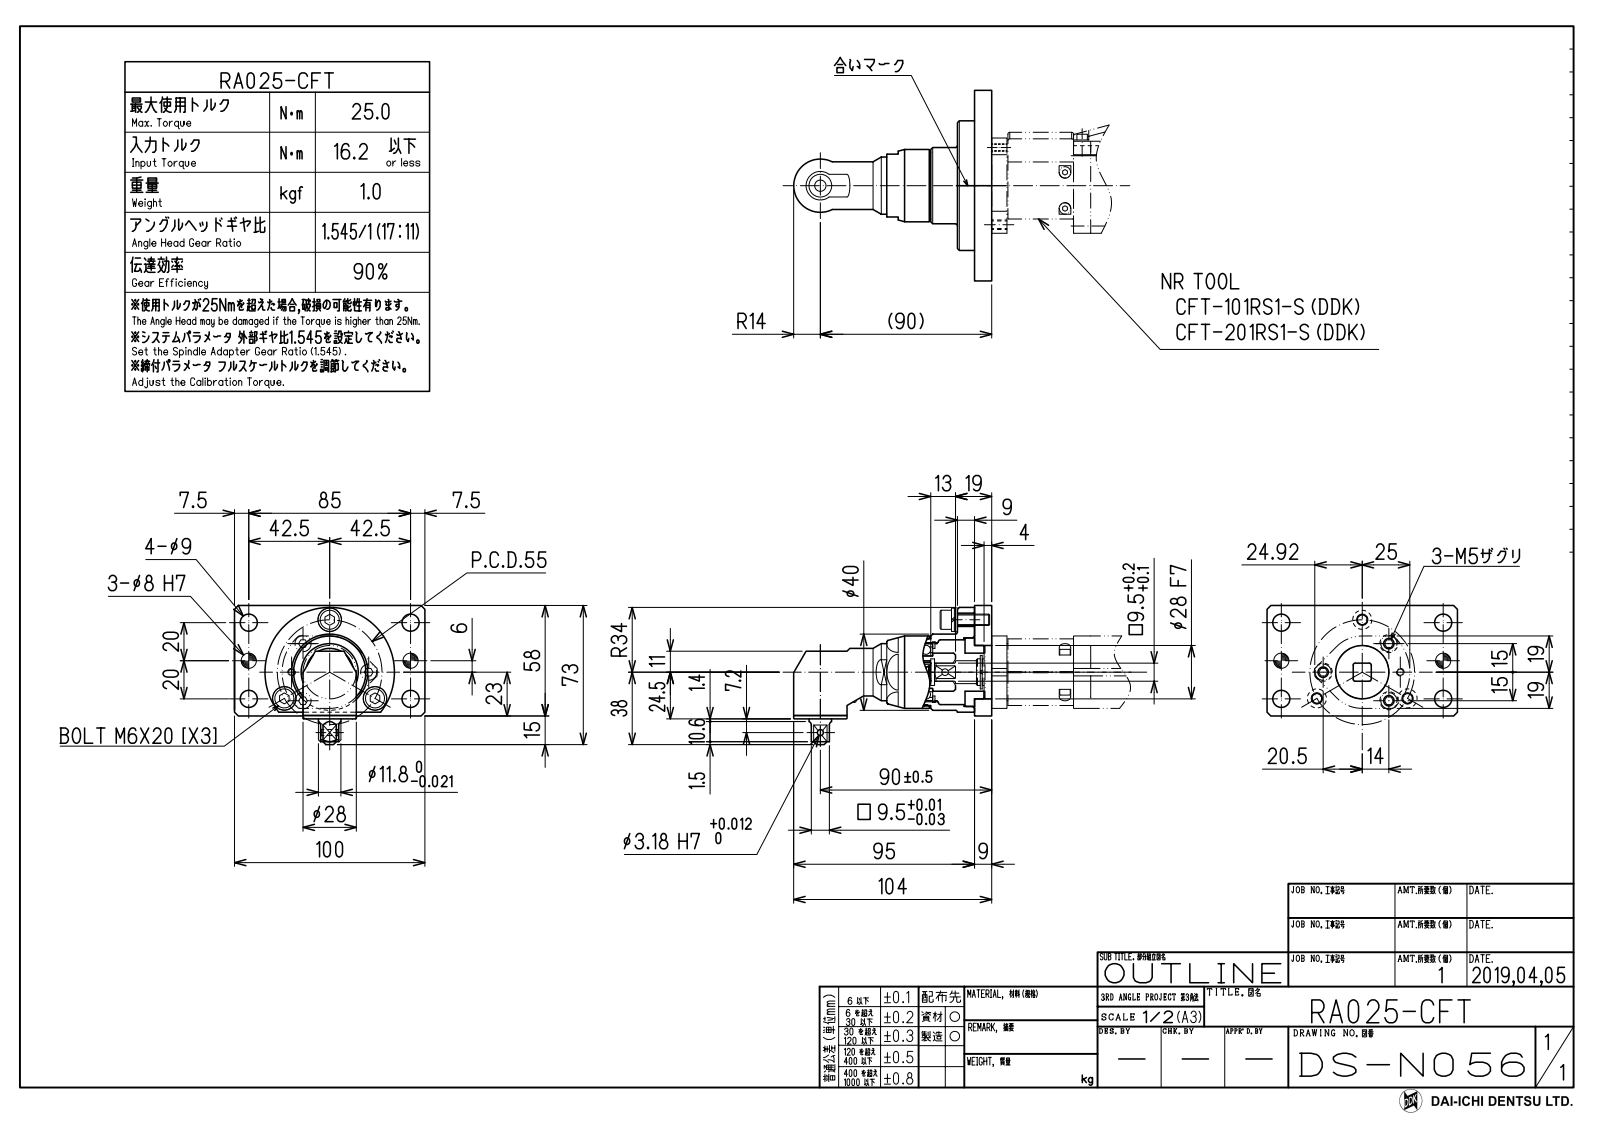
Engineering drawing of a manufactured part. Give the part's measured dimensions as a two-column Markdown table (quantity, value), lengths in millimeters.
| quantity | value |
| --- | --- |
| part name | RA025-CFT(DS-N056)_Shrinkwrap_2 |
| STEP written by | Autodesk Inventor 2019 (AUTOMOTIVE_DESIGN) |
| units | millimeters |
| bodies | 1 solid, 319 faces (164 planar, 85 cylindrical, 70 other) |
| overall size | 104 × 100 × 72.49 |
| volume | 134 246 mm³ |
| surface area | 37 613 mm² |
| round holes (diameter × count) | 3.6 × 4, 9 × 4, 4.92 × 3, 5.5 × 3, 6.1 × 3, 6.4 × 3, 9.5 × 3, 8 × 2, 2 × 1, 3.18 × 1, 4.7 × 1, 12 × 1 |
| round bosses / shafts (diameter × count) | 12.5 × 3, 12.2 × 3, 10 × 3, 6 × 3, 40 × 1, 38 × 1, 35 × 1, 28 × 1 |
| partial cylindrical surfaces (radius × count) | 3.2 × 6, 1 × 4, 9.45 × 1, 9.55 × 1, 13 × 1, 24.3 × 1, 30.7 × 1, 34 × 1 |
| main face-to-face distances | 9, 18, 14, 5, 4, 58, 3.5, 2, 1.5, 32 |
| hole center spacings | 9.5, 13.44, 20, 47.63, 87.32, 27.5, 44.75, 85 |
